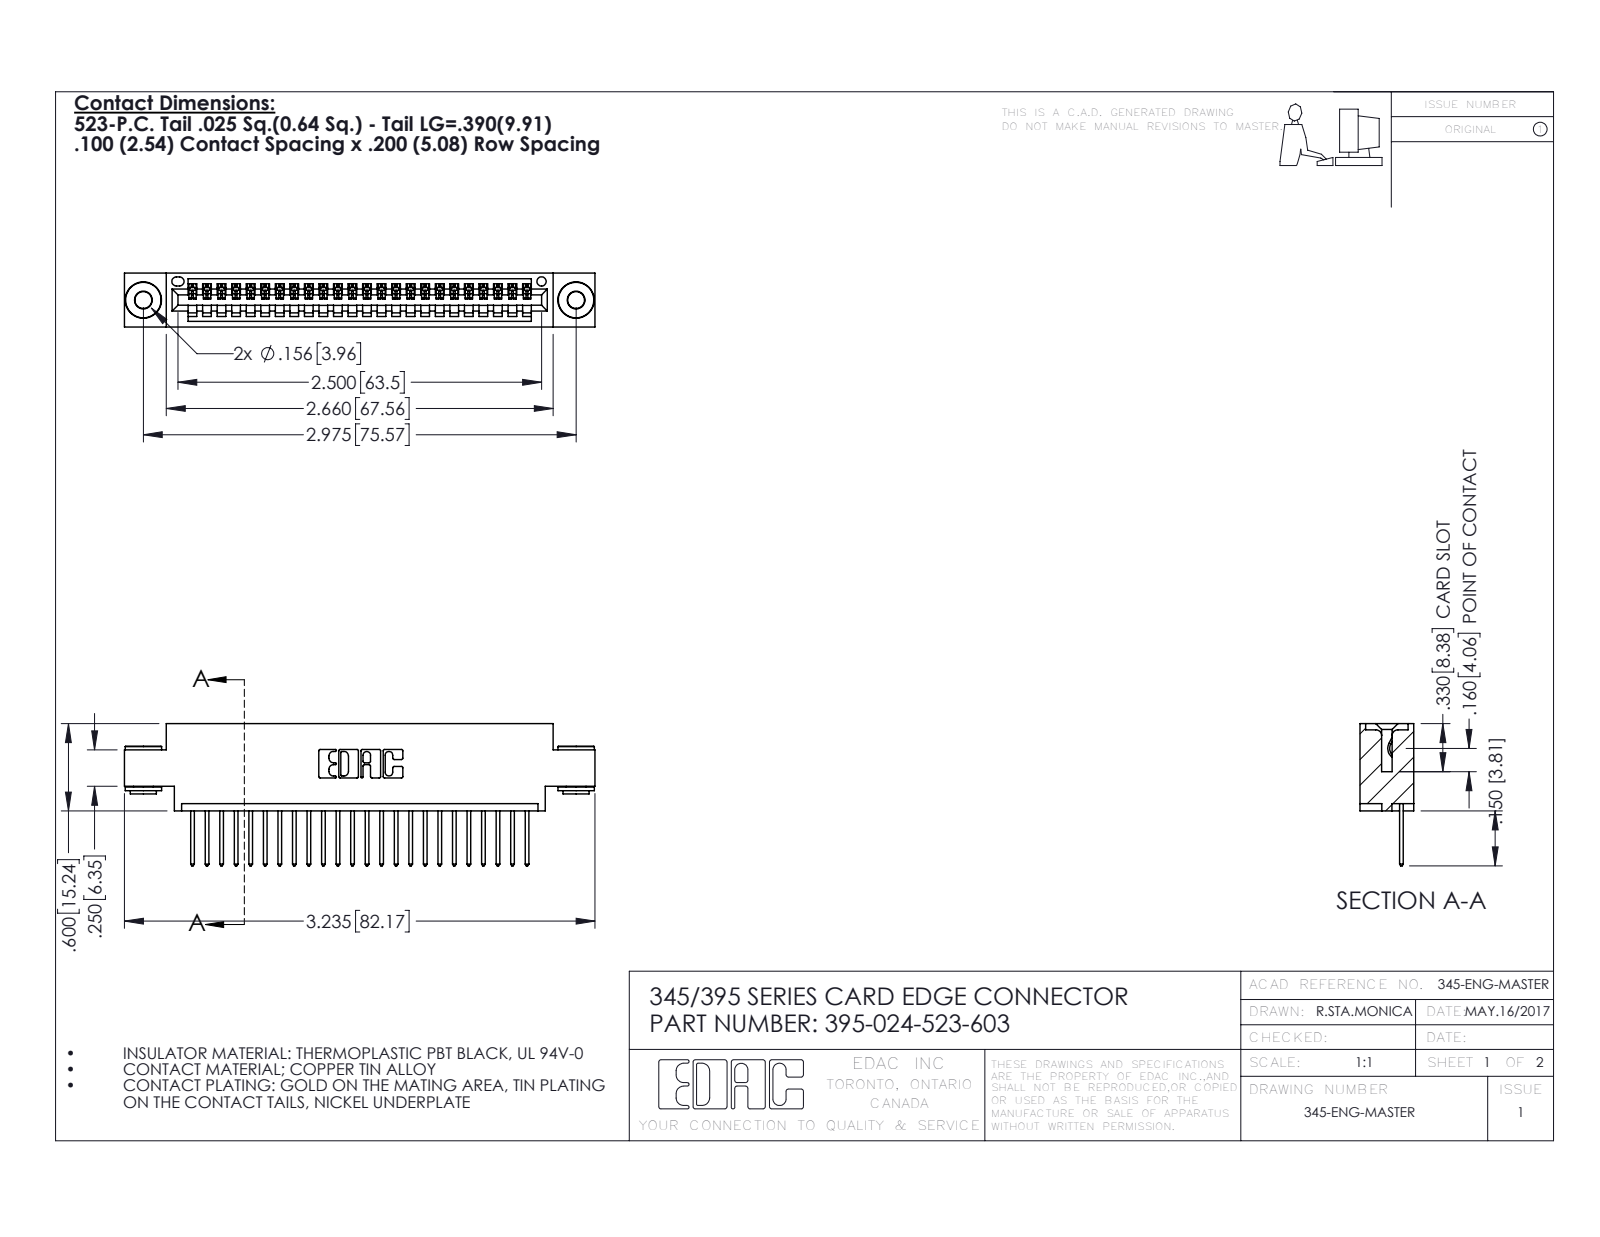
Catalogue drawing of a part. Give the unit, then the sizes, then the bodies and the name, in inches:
Units: inches
Overall size (bounding box): 3.235 × 0.977 × 0.37
Round holes (diameter × count): ⌀0.116 ×2, ⌀0.156 ×2, ⌀0.064 ×1
Round bosses / shafts (diameter × count): ⌀0.25 ×2, ⌀0.18 ×2, ⌀0.136 ×2
Partial cylindrical surfaces — rounded edges, fillets, slot ends (radius × count): R0.006 ×48, R0.01 ×48, R0.01 ×22, R0.007 ×6, R0.031 ×6, R0.026 ×3, R0.031 ×2, R0.04 ×2
Main face-to-face distances: 0.072, 0.298, 0.37, 0.2, 0.098, 0.272, 0.025, 0.225, 0.175, 0.15
Hole centre spacings: 0.27, 2.741, 2.975
Volume: 0.461 in³ · Surface area: 15.75 in²
Bodies: 27 solids, 1560 faces (1054 planar, 498 cylindrical, 8 other)
Part name (STEP PRODUCT): 345-292-001_345-293-123; 345 Part_0.170 Offset - 0.156 Dia-TH; 345-250-002_345-250-002-102; 395-024-523-603
STEP written by: SolidWorks 2016 (CONFIG_CONTROL_DESIGN)
